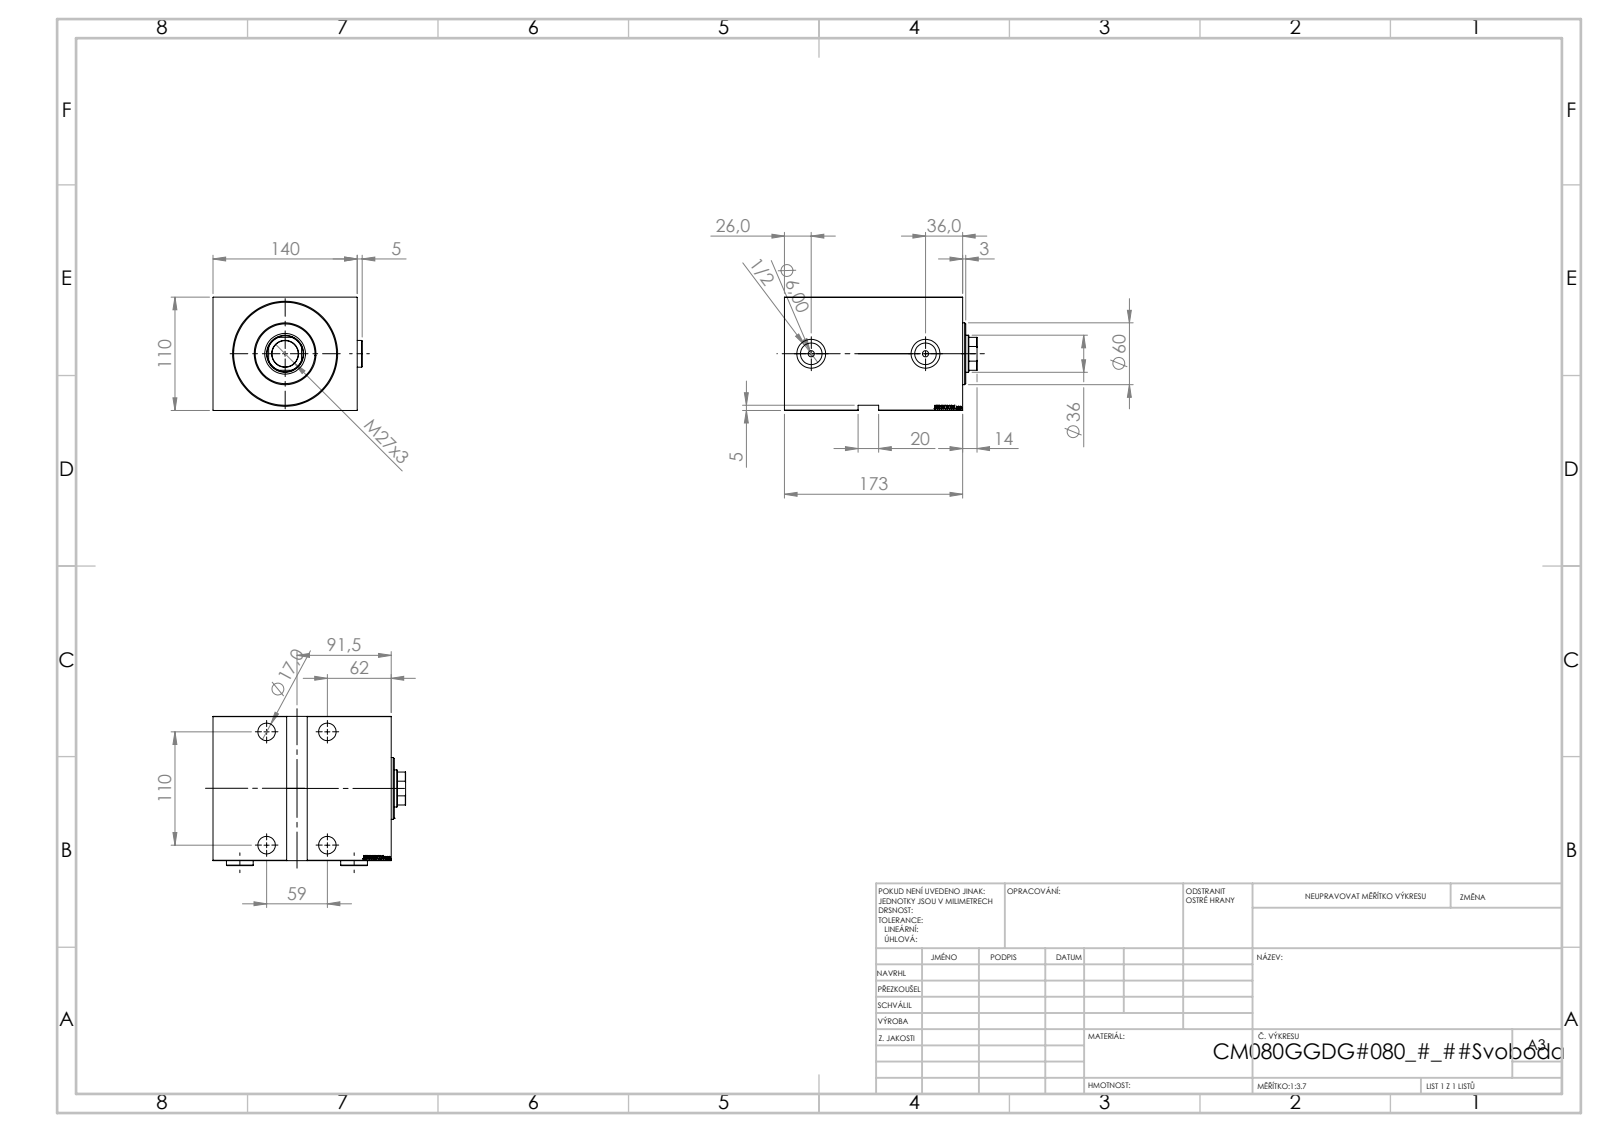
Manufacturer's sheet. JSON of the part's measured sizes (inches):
{"part_name": "V450CM_VC_G; Zatka_OIL_PORT; V450CM_G_VCP; V450CM_G_Body", "step_written_by": "SolidWorks 2019 (CONFIG_CONTROL_DESIGN)", "units": "inches", "bodies": {"solids": 5, "faces": 912, "planar": 446, "cylindrical": 68, "other": 398}, "overall_size": [7.362, 5.705, 4.331], "volume_in3": 131.2, "surface_area_in2": 379.1, "round_holes": [[0.669, 4], [0.984, 4], [0.236, 2], [0.825, 2], [1.102, 2], [1.004, 1], [1.417, 1], [1.555, 1], [3.15, 1], [3.228, 1], [3.937, 1]], "round_bosses_or_shafts": [[1.024, 2], [2.362, 1]], "partial_cylinders_radius": [[0.689, 1]], "face_to_face_distances": [4.331, 5.512, 0.197, 6.811, 0.827, 5.984, 6.614, 5.787, 3.11, 2.283], "hole_center_spacings": [2.323, 4.331, 4.914, 4.37]}
